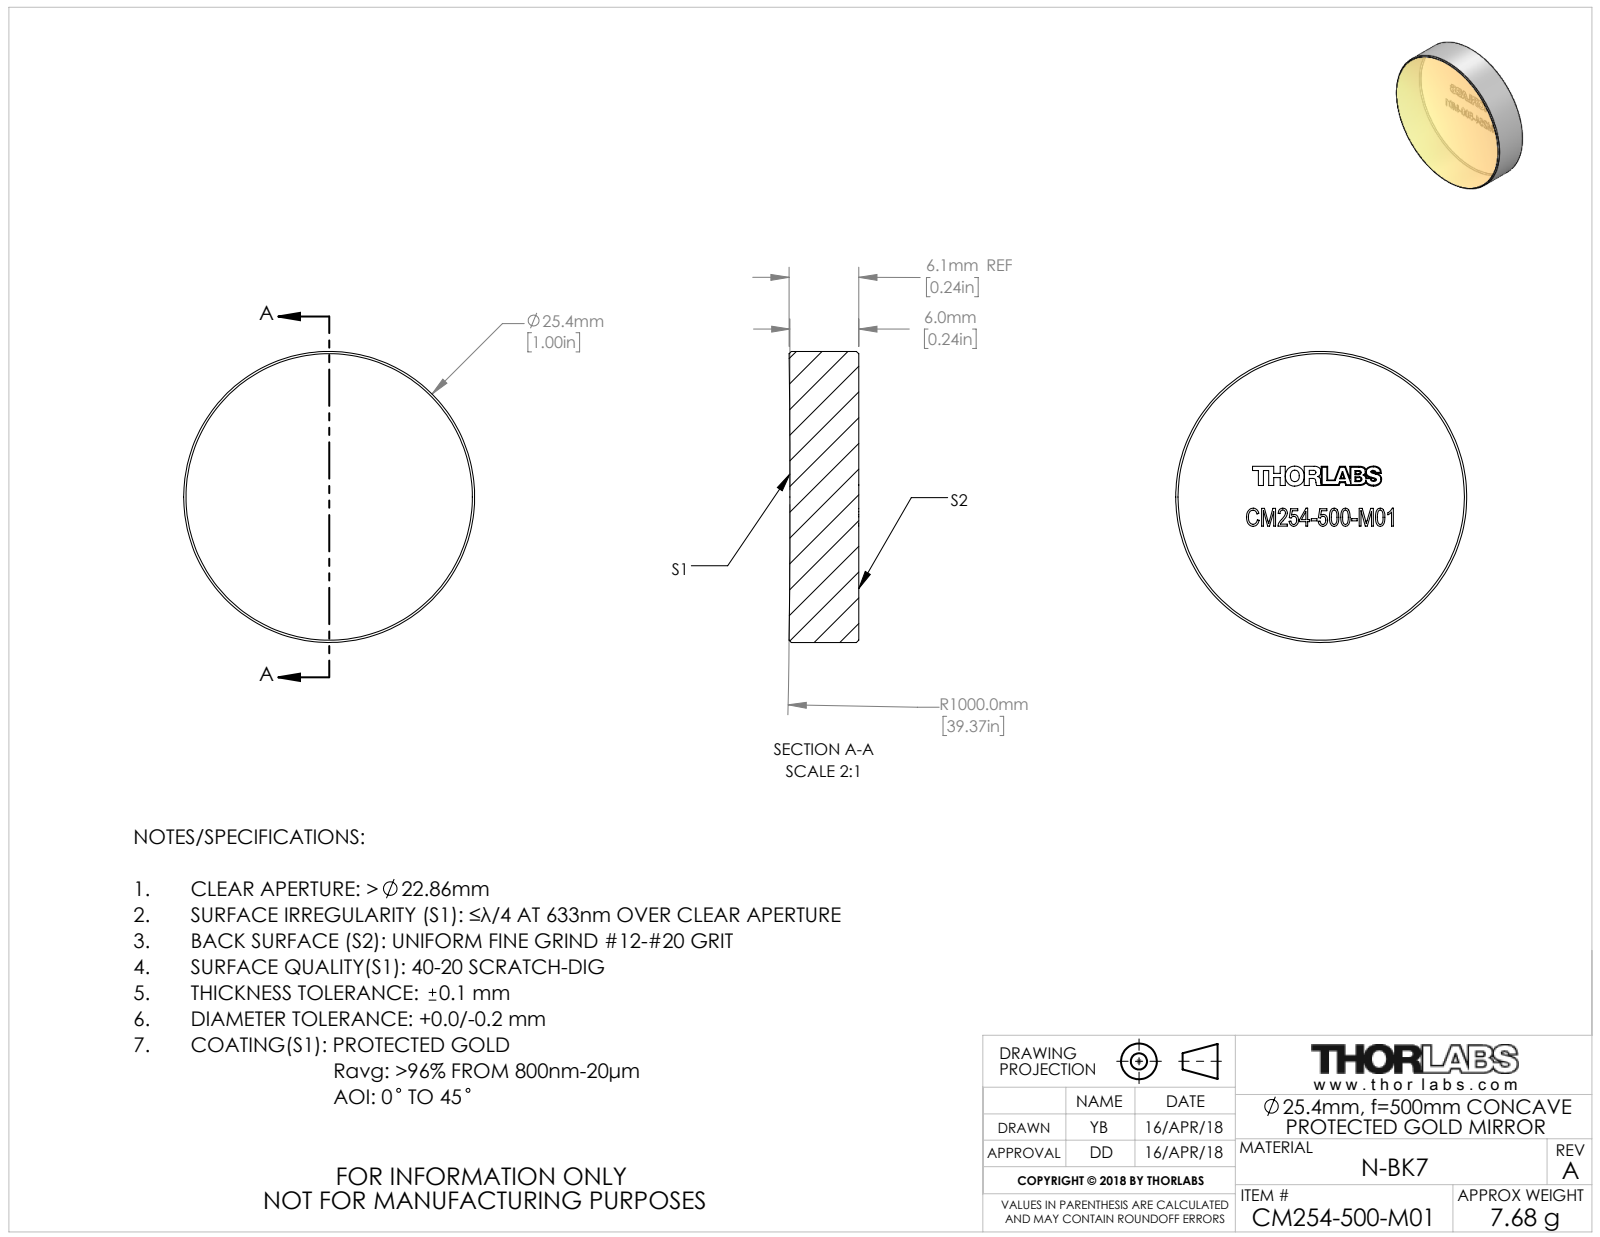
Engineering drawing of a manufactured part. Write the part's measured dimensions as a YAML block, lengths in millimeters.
part_name: "TTN153303-E0W"
step_written_by: "SolidWorks 2018 (CONFIG_CONTROL_DESIGN)"
units: millimeters
bodies: {solids: 1, faces: 41, planar: 33, cylindrical: 2, other: 6}
overall_size: [25.4, 25.4, 6.08]
volume: 3058
surface_area: 1480
round_bosses_or_shafts:
  - {diameter: 25.4, count: 1}
